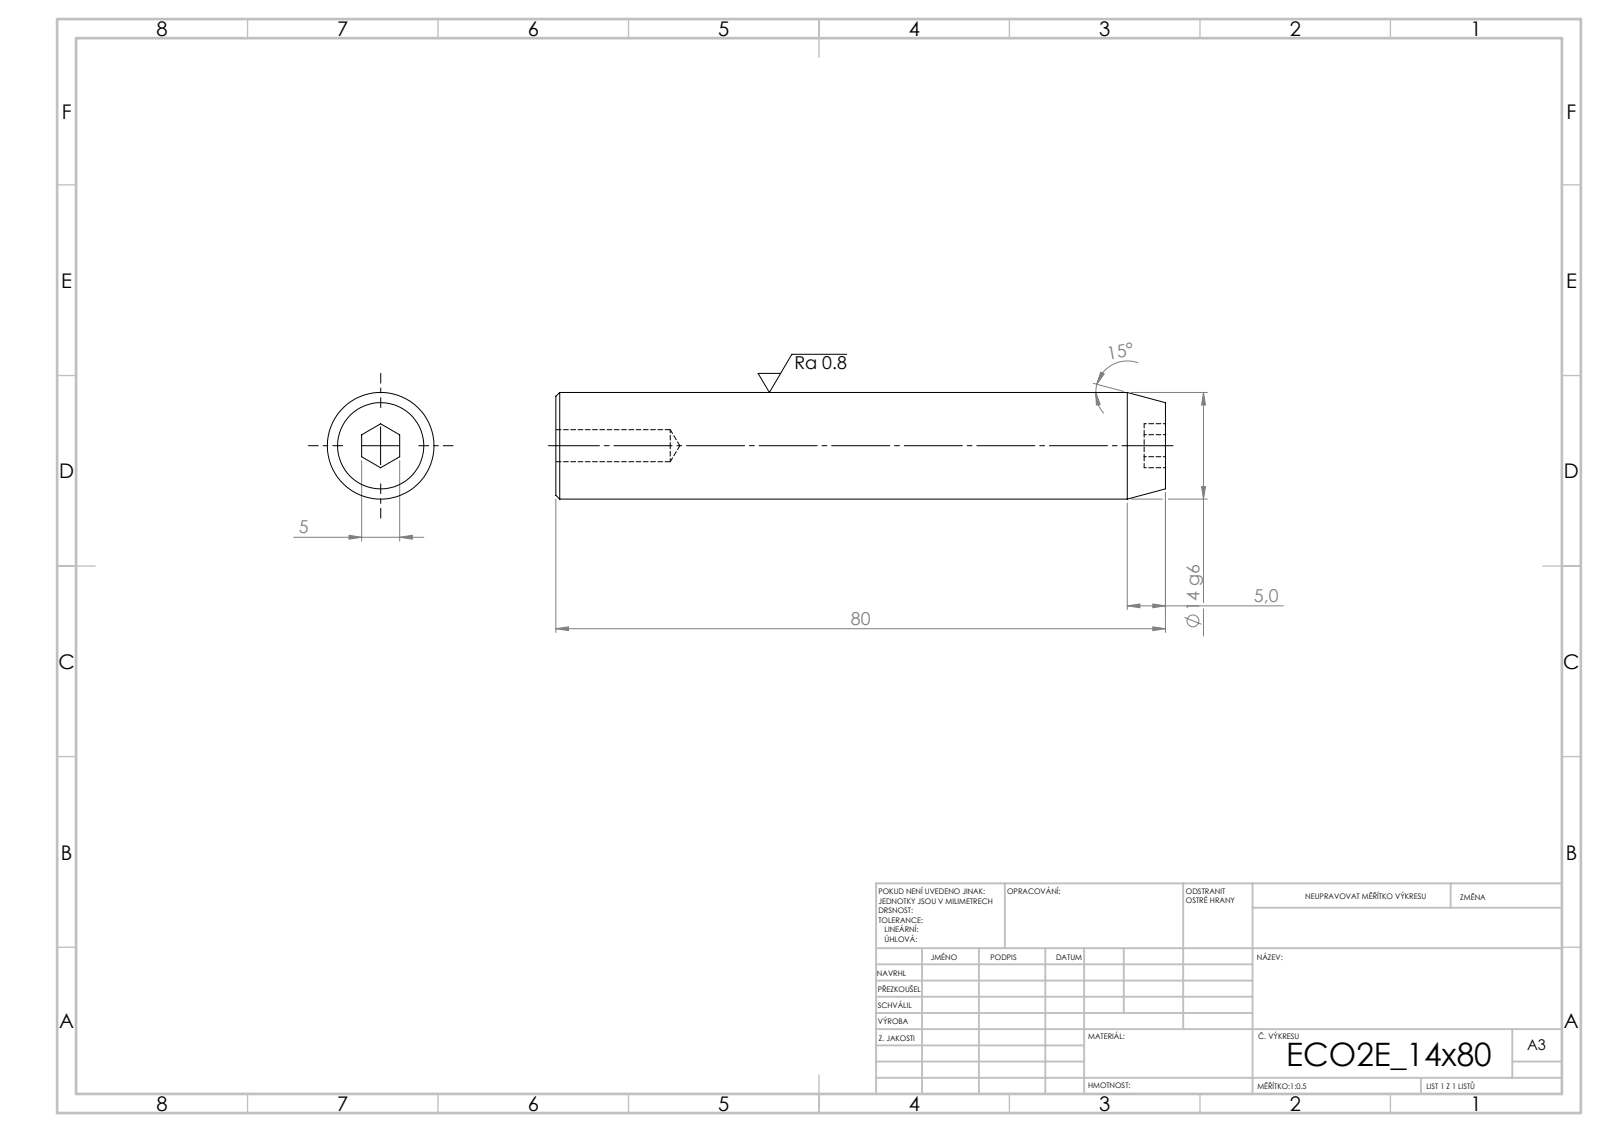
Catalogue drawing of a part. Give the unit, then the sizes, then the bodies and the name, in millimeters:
Units: millimetres
Overall size (bounding box): 80 × 14 × 14
Round holes (diameter × count): ⌀4.2 ×1
Round bosses / shafts (diameter × count): ⌀14 ×1
Main face-to-face distances: 80, 5, 2.8, 77.2
Volume: 11 897 mm³ · Surface area: 3 995 mm²
Bodies: 1 solid, 19 faces (9 planar, 4 cylindrical, 6 other)
STEP written by: SolidWorks 2019 (CONFIG_CONTROL_DESIGN)
